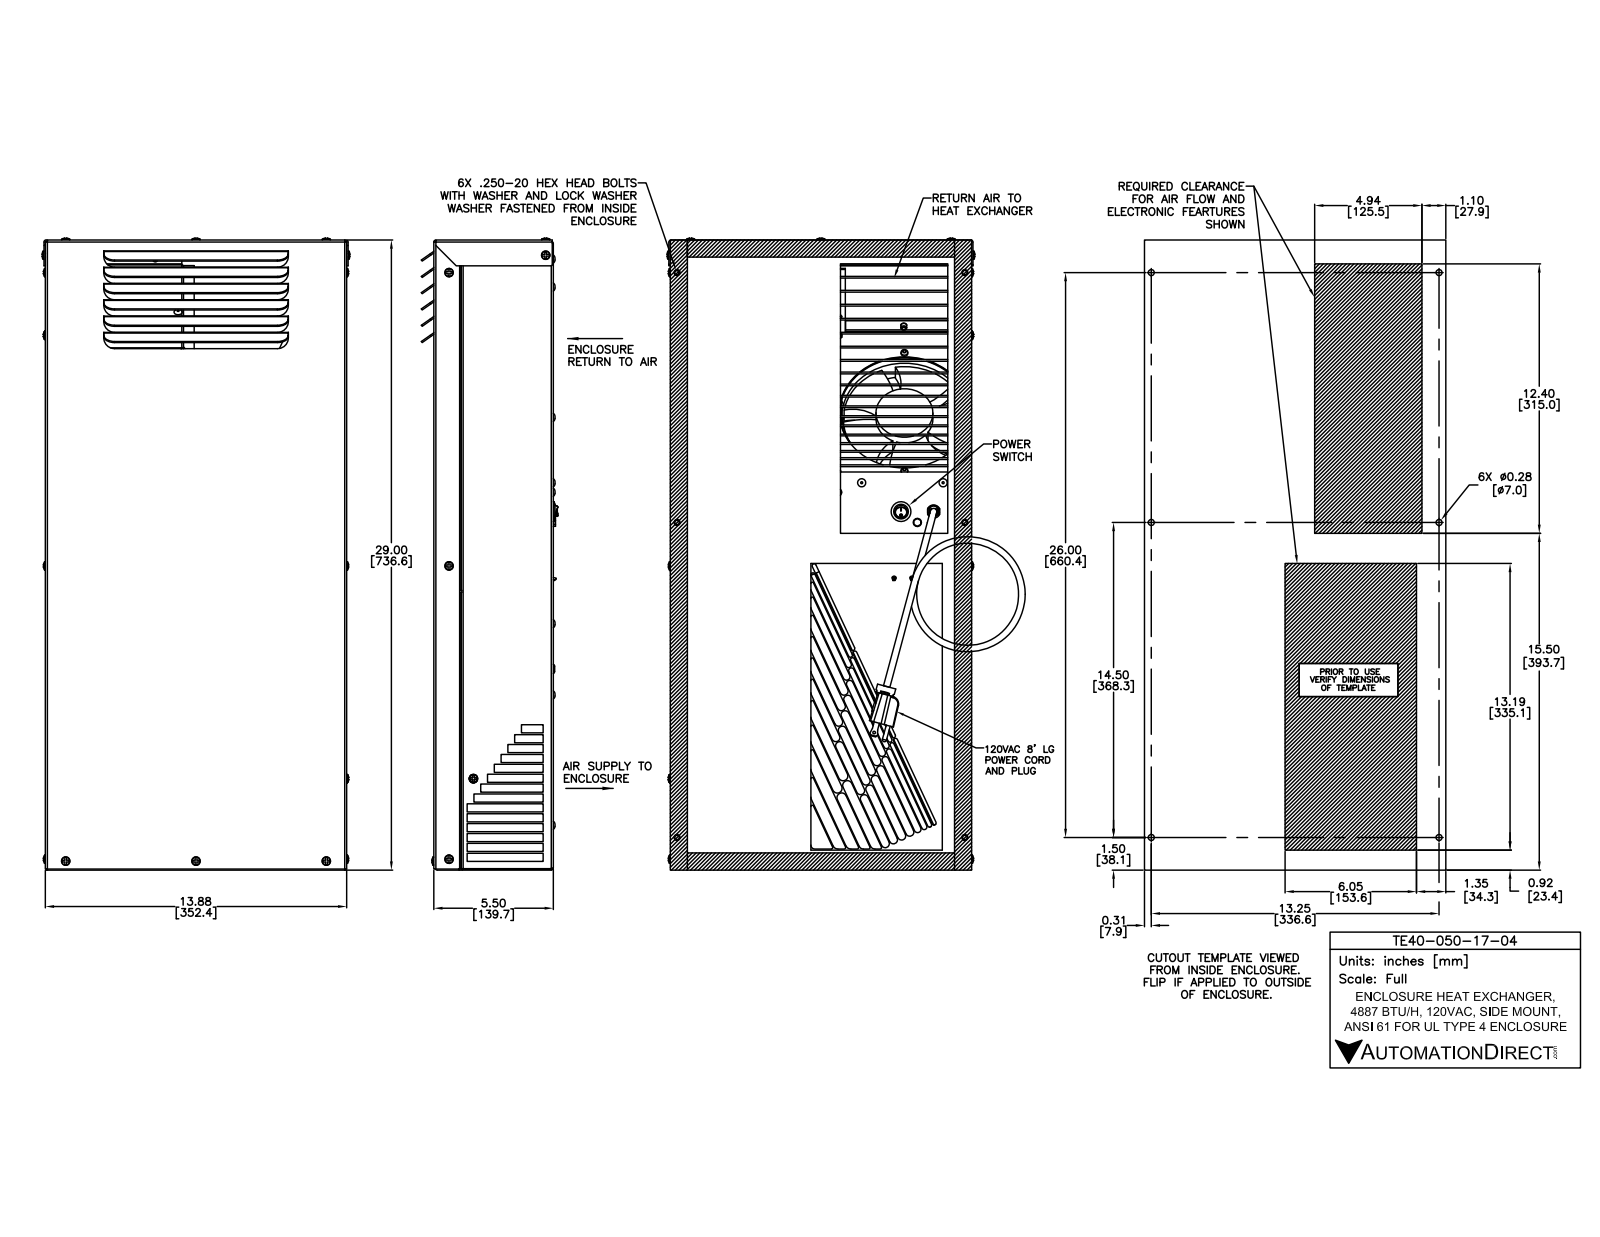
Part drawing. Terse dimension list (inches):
name: TE40-050-17-04
written by: SolidWorks 2017 (AUTOMOTIVE_DESIGN)
unit: in
bodies: 125 solids, 3479 faces (1943 planar, 1134 cylindrical, 402 other)
size: 29.094 × 16.5 × 9.509
volume: 338.4 in³; area: 5 267 in²
holes: 21× ⌀0.193, 17× ⌀0.219, 15× ⌀0.188, 14× ⌀0.159, 11× ⌀0.203, 9× ⌀0.515, 8× ⌀0.109, 8× ⌀0.173, 8× ⌀0.5, 8× ⌀0.885, 6× ⌀0.201, 6× ⌀0.272
bosses: 15× ⌀0.27, 14× ⌀0.19, 8× ⌀1, 8× ⌀0.935, 6× ⌀0.564, 6× ⌀0.326, 6× ⌀0.325, 6× ⌀0.248
rounds: 96× R0.01, 96× R0.015, 46× R0.031, 46× R0.093, 28× R0.06, 24× R0.047, 19× R0.188, 17× R0.063
face distances: 0.062, 0.062, 5.5, 5.438, 5.376, 5.438, 13.813, 0.25, 6.25, 7.563
hole spacings: 1.25, 2.5, 3.75, 3.189, 3.189, 3.189, 2.896, 6.378
